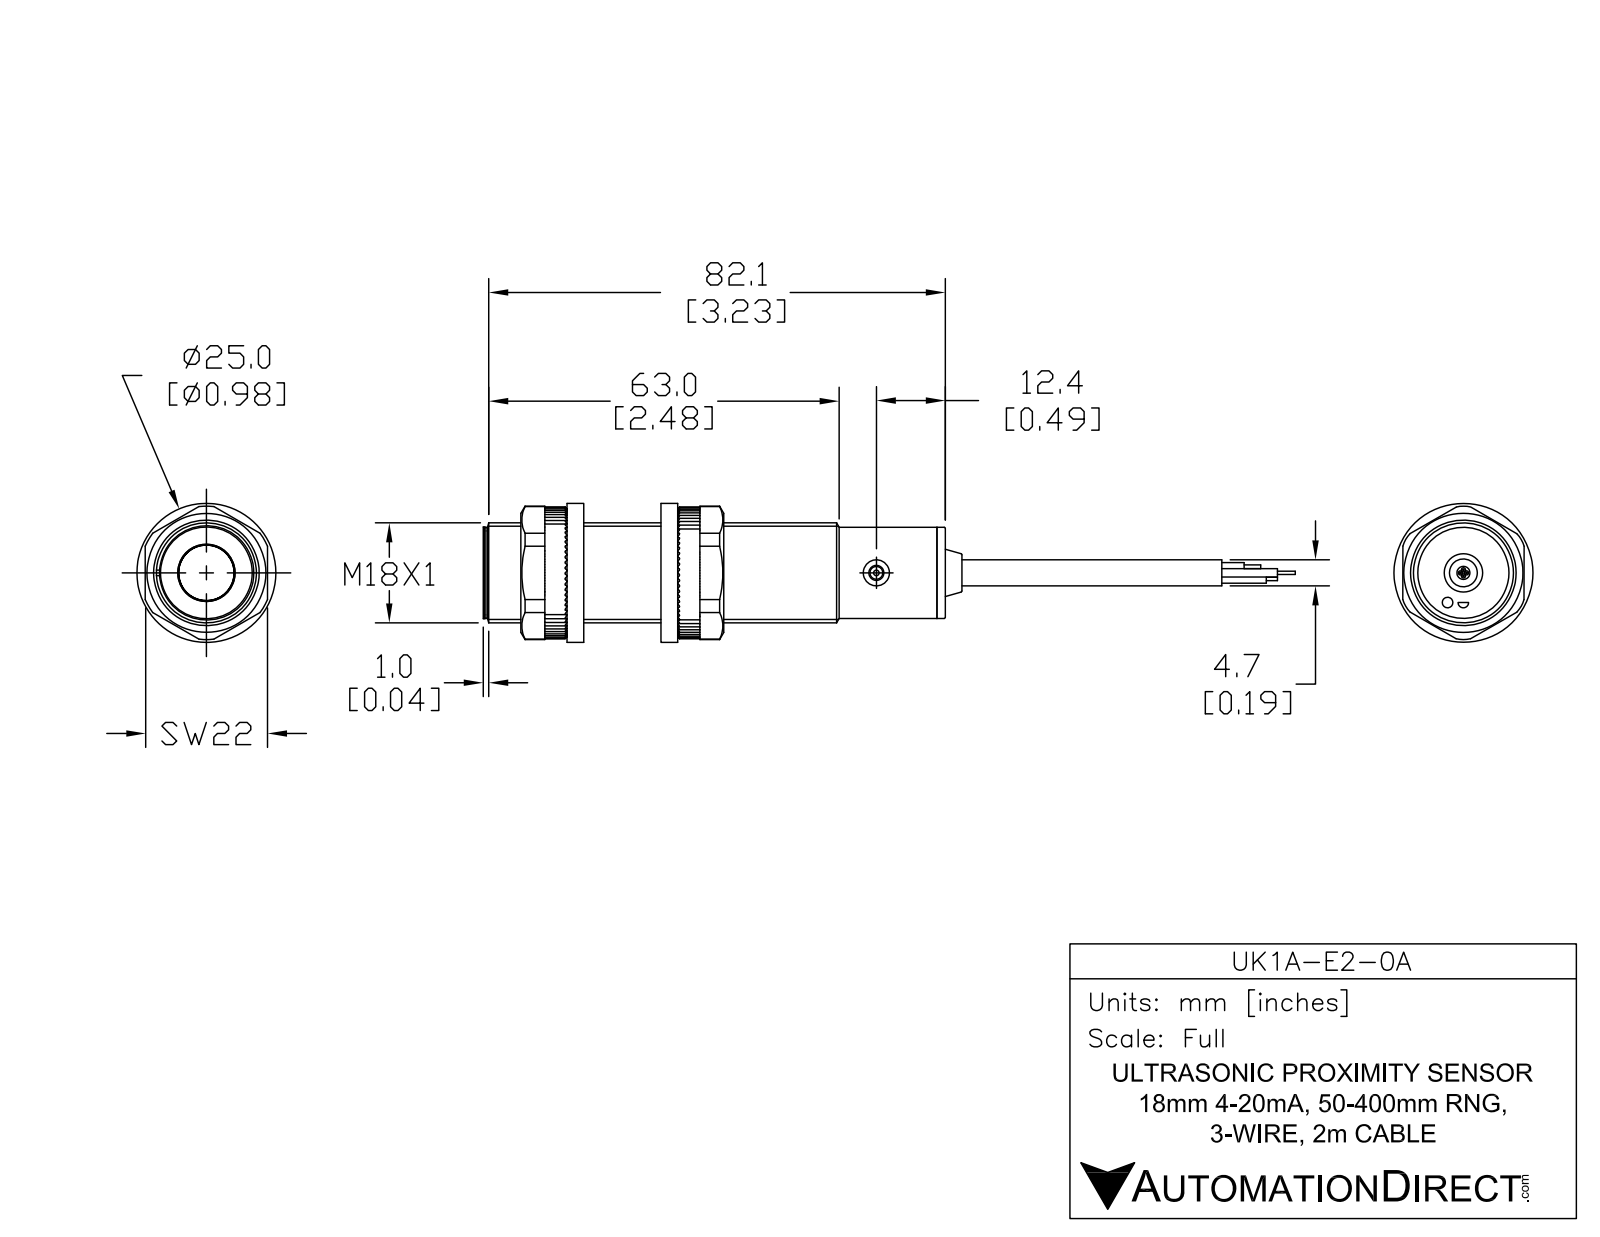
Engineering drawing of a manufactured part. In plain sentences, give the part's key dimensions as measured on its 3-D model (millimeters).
The part is named "UK1A-E2-0A". Its 3-D file was written by "SolidWorks 2017 (AUTOMOTIVE_DESIGN)". It is 6 solids with 55 faces: 17 planar, 24 cylindrical and 14 other. Overall it measures 122.7 by 18 by 18 millimeters. Its volume is 21 060 cubic millimeters and its surface area 6 897 square millimeters. Round holes: 2 of diameter 4.7, 1 of diameter 2.7. Round bosses or shafts: 1 of diameter 18, 1 of diameter 16.4, 1 of diameter 15.8, 1 of diameter 9.5, 1 of diameter 4.8, 1 of diameter 2.3. The main face-to-face distances are 81.1, 82.6, 1.5, 1, 82.1, 83.6, 1, 82.1, 83.6, 82.7.
